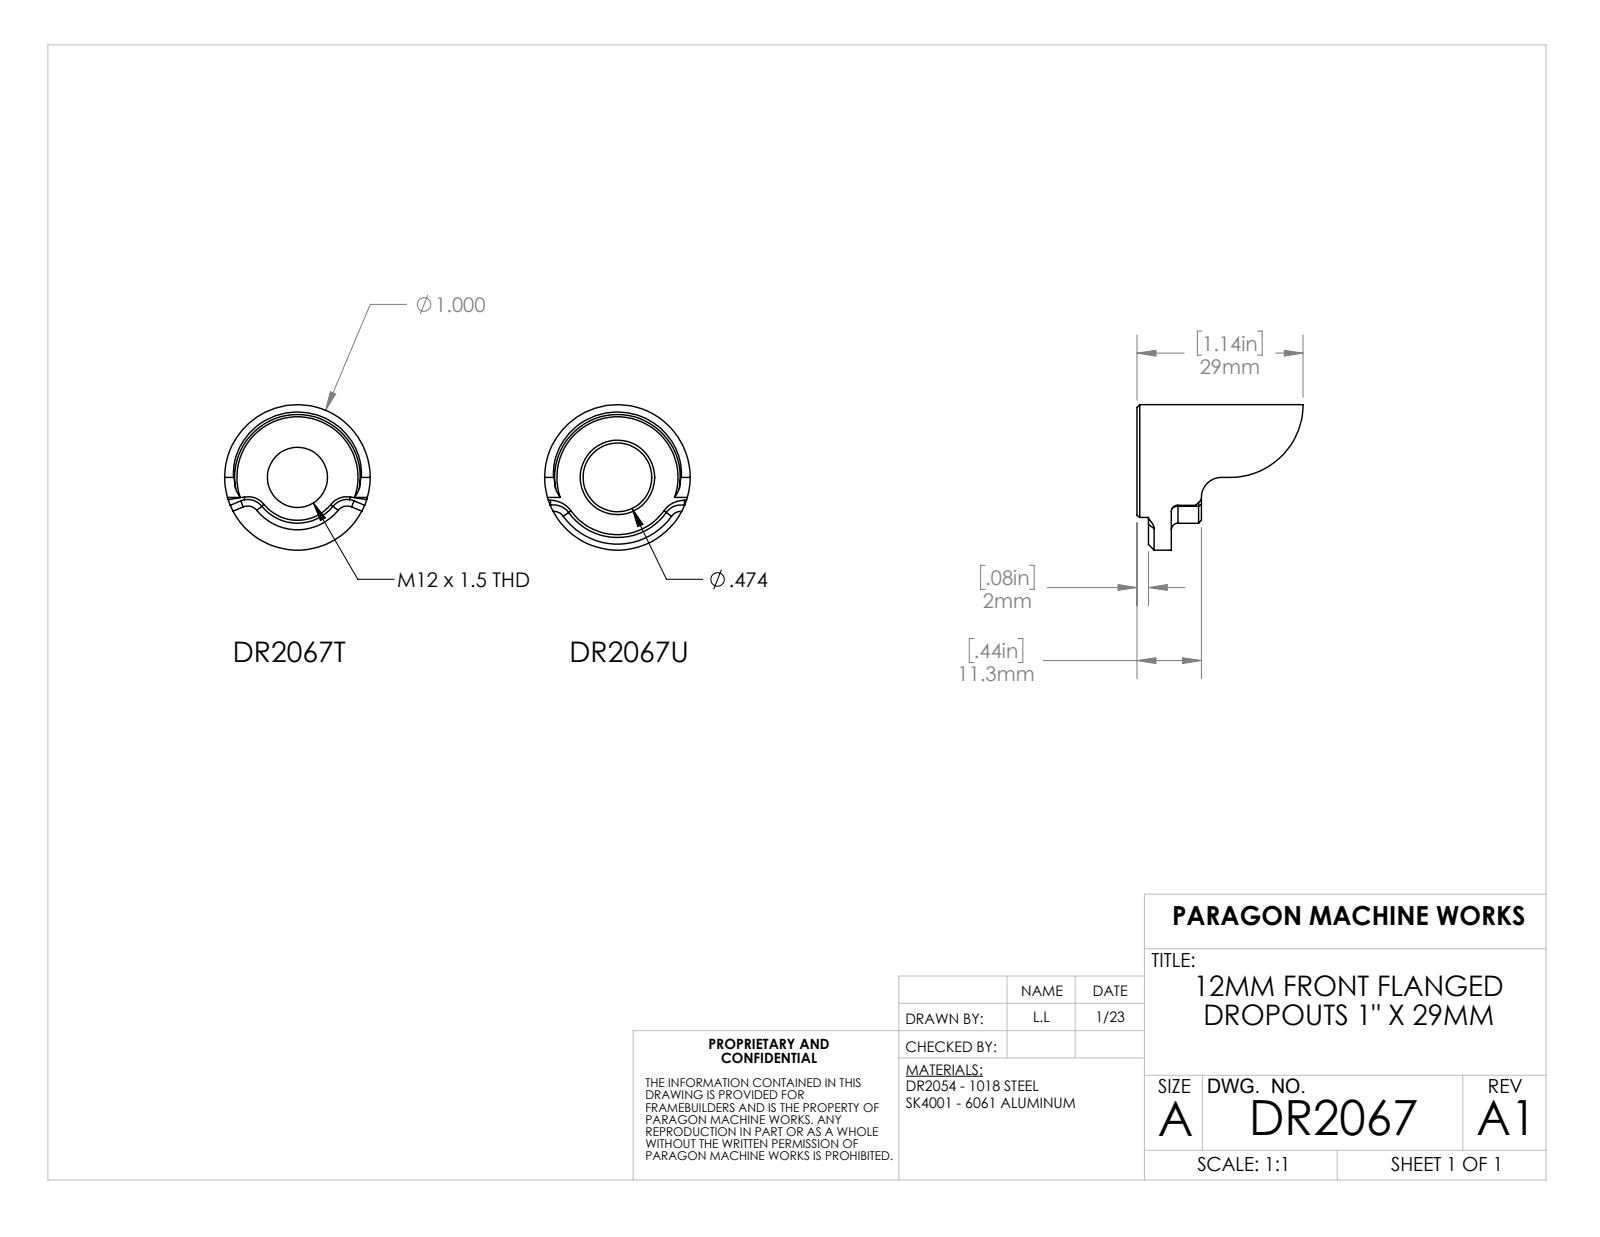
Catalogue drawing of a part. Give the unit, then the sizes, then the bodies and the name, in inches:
Units: inches
Overall size (bounding box): 3.2 × 1.142 × 1
Round holes (diameter × count): ⌀0.472 ×2, ⌀0.413 ×1
Round bosses / shafts (diameter × count): ⌀1 ×2
Partial cylindrical surfaces — rounded edges, fillets, slot ends (radius × count): R0.098 ×4, R0.125 ×4, R0.045 ×2, R0.378 ×2, R0.138 ×1, R0.315 ×1, R0.413 ×1, R0.5 ×1
Main face-to-face distances: 0.364, 0.079, 0.443, 0.236, 0.157, 0.207, 0.138, 0.059, 0.098, 0.305
Hole centre spacings: 2.2
Volume: 0.546 in³ · Surface area: 9.967 in²
Bodies: 2 solids, 91 faces (23 planar, 30 cylindrical, 38 other)
Part name (STEP PRODUCT): DR2067_DR2067T; DR2067_DR2067U; DR2067
STEP written by: SolidWorks 2022 (AUTOMOTIVE_DESIGN)
